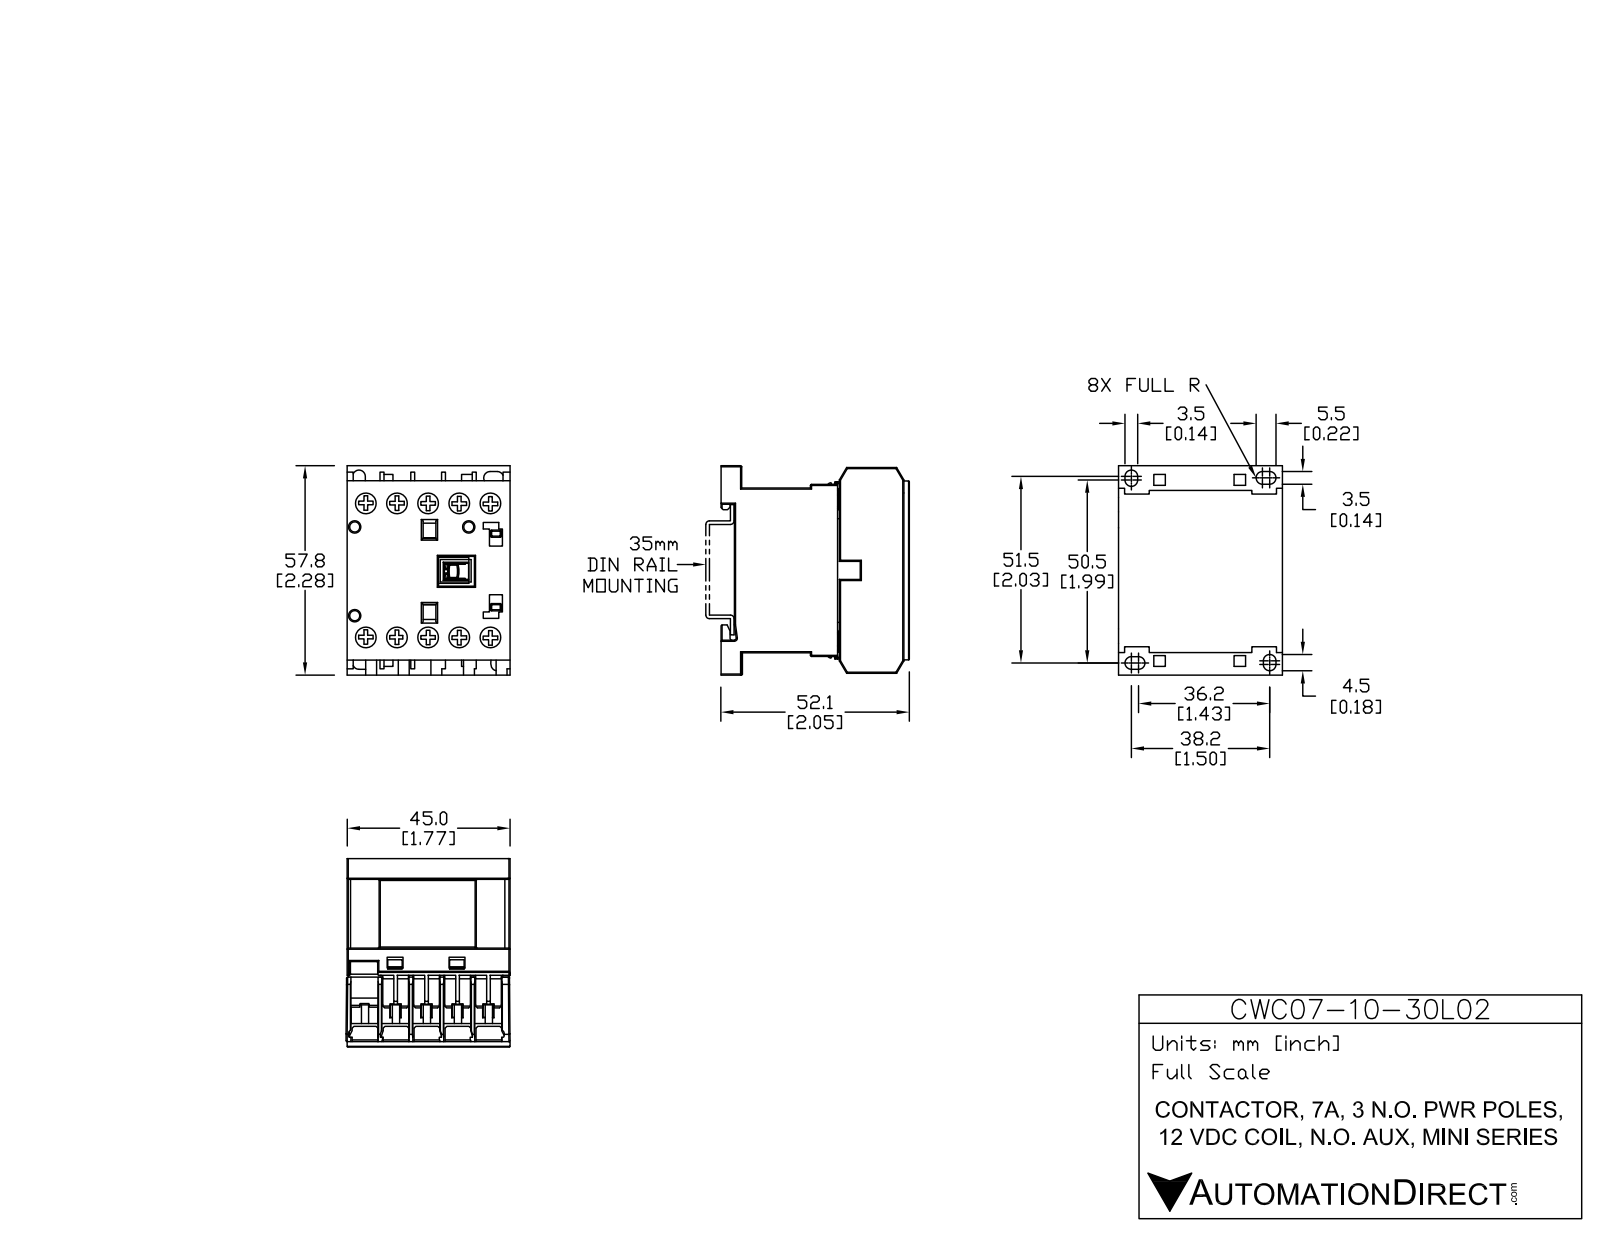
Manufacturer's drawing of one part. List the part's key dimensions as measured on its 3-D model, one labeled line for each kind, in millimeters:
Part name (STEP PRODUCT): CWC07-10-30L02
STEP written by: SolidWorks 2013 (AUTOMOTIVE_DESIGN)
Units: millimetres
Bodies: 15 solids, 535 faces (445 planar, 90 cylindrical, 0 other)
Overall size (bounding box): 58.04 × 52.12 × 45.75
Volume: 97 133 mm³ · Surface area: 30 437 mm²
Round holes (diameter × count): ⌀6.2 ×10, ⌀2.8 ×3
Round bosses / shafts (diameter × count): ⌀5.9 ×10
Partial cylindrical surfaces — rounded edges, fillets, slot ends (radius × count): R0.3 ×20, R1.72 ×6, R1.73 ×2, R0.32 ×1, R0.42 ×1, R0.55 ×1
Main face-to-face distances: 8.25, 45.5, 1.25, 16.5, 9.5, 5.5, 17.75, 5.13, 10.63, 7
Hole centre spacings: 8.55, 37.94, 17.1, 40.72, 36.96, 25.65, 44.99, 6.91
